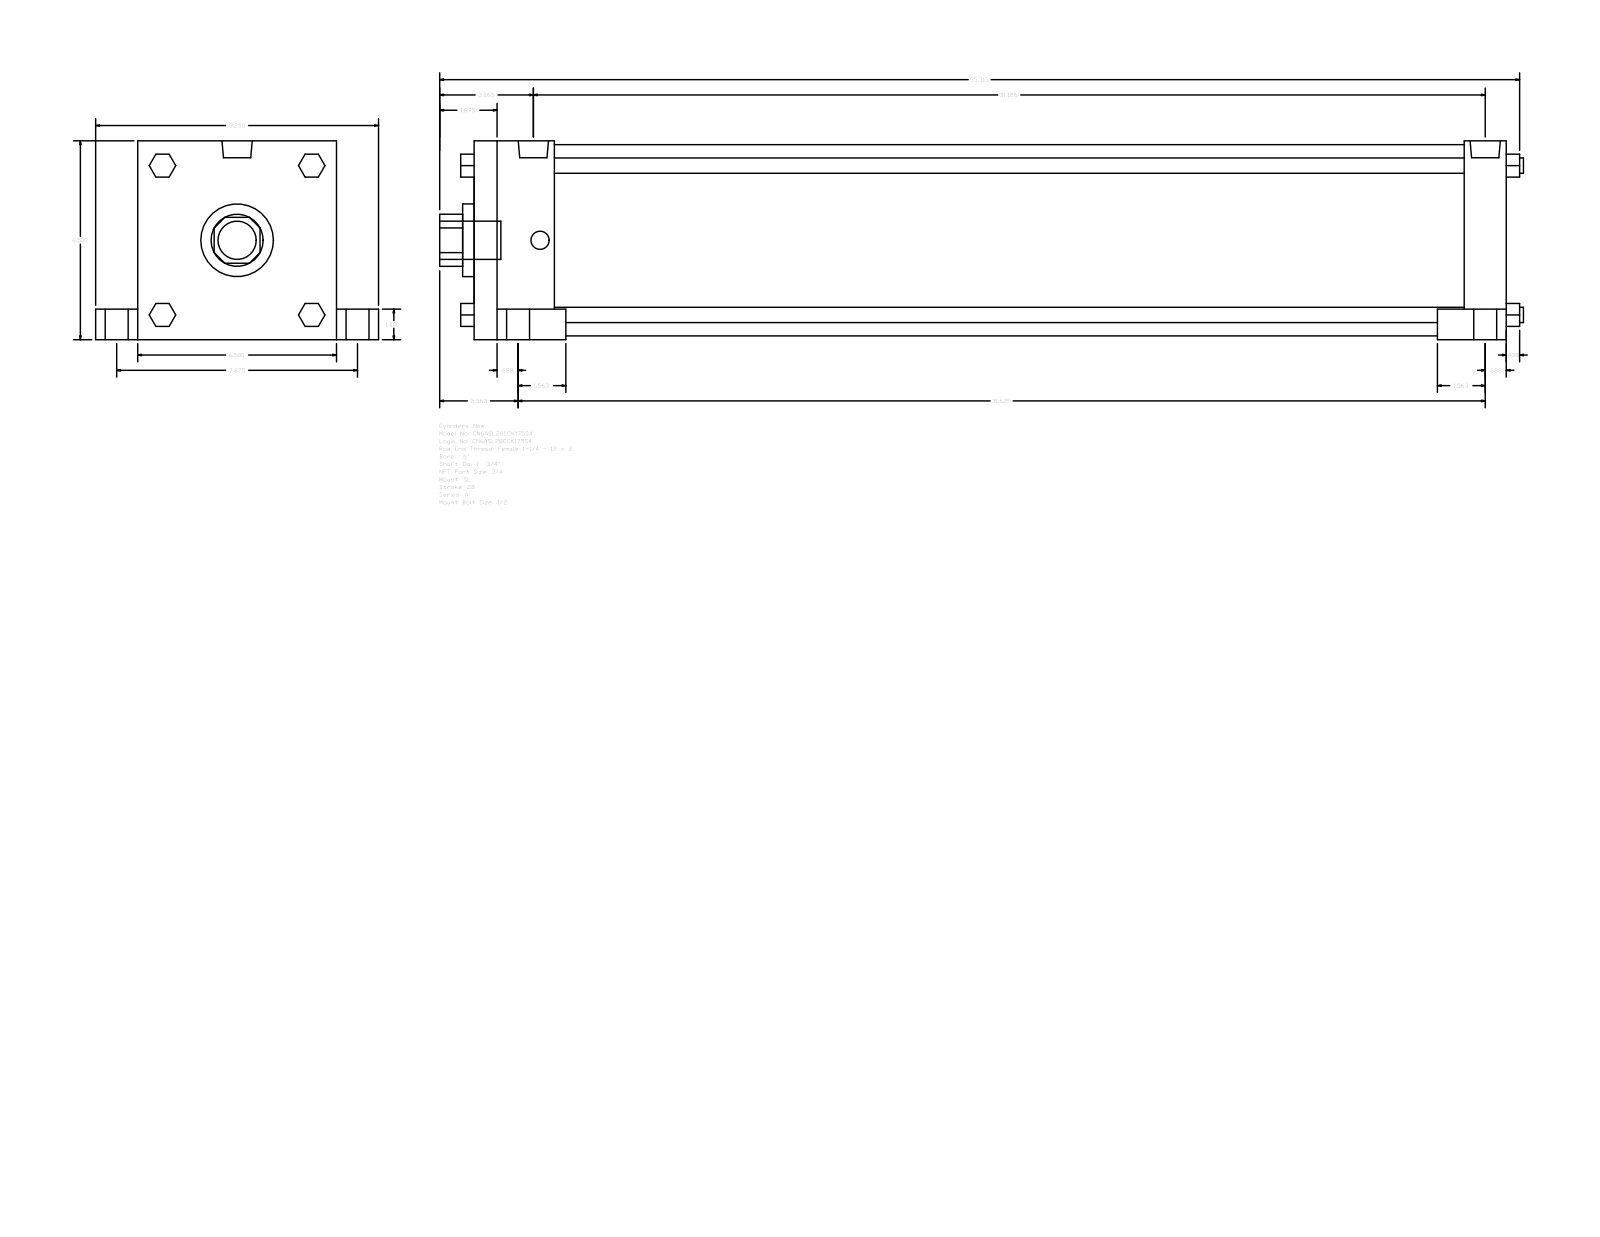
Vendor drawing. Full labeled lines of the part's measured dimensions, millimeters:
Part name (STEP PRODUCT): A_SL__0600_1.75
STEP written by: GSSL Pune (CONFIG_CONTROL_DESIGN)
Units: millimetres
Bodies: 0 solids, 150 faces (114 planar, 36 cylindrical, 0 other)
Overall size (bounding box): 900.11 × 234.95 × 165.1
Round holes (diameter × count): ⌀44.45 ×1, ⌀60.33 ×1, ⌀158.75 ×1
Round bosses / shafts (diameter × count): ⌀25.4 ×4, ⌀19.05 ×4, ⌀15.08 ×4, ⌀12.7 ×4, ⌀25.12 ×2, ⌀31.75 ×1
Partial cylindrical surfaces — rounded edges, fillets, slot ends (radius × count): R21.63 ×1
Main face-to-face distances: 165.1, 857.26, 66.68, 790.58, 822.33, 755.65, 34.93, 34.92, 25.4, 139.7
